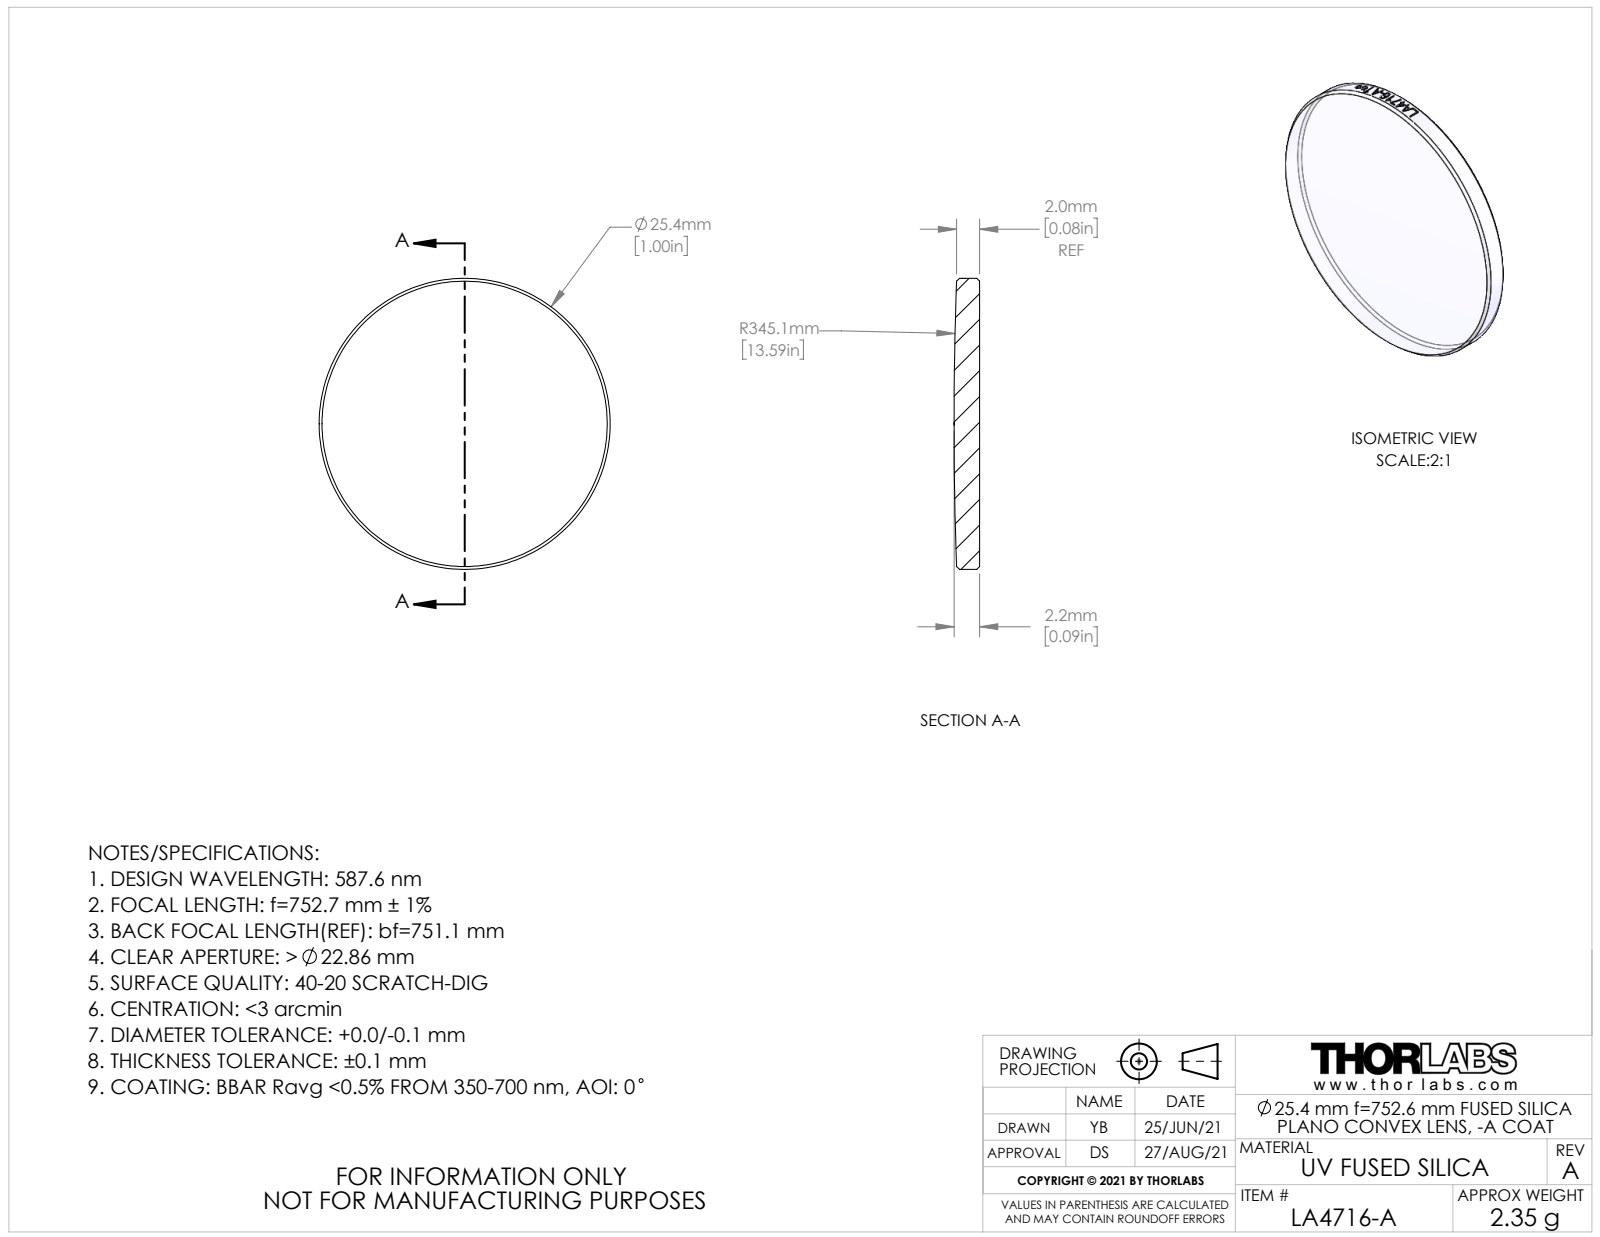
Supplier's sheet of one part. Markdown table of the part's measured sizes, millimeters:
| quantity | value |
| --- | --- |
| part name | CTN017561; CTN017533-E0W |
| STEP written by | SolidWorks 2018 (AUTOMOTIVE_DESIGN) |
| units | millimeters |
| bodies | 1 solid, 25 faces (1 planar, 18 cylindrical, 6 other) |
| overall size | 25.4 × 25.4 × 2.23 |
| volume | 1 067 mm³ |
| surface area | 1 150 mm² |
| round bosses / shafts (diameter × count) | 25.4 × 1 |
